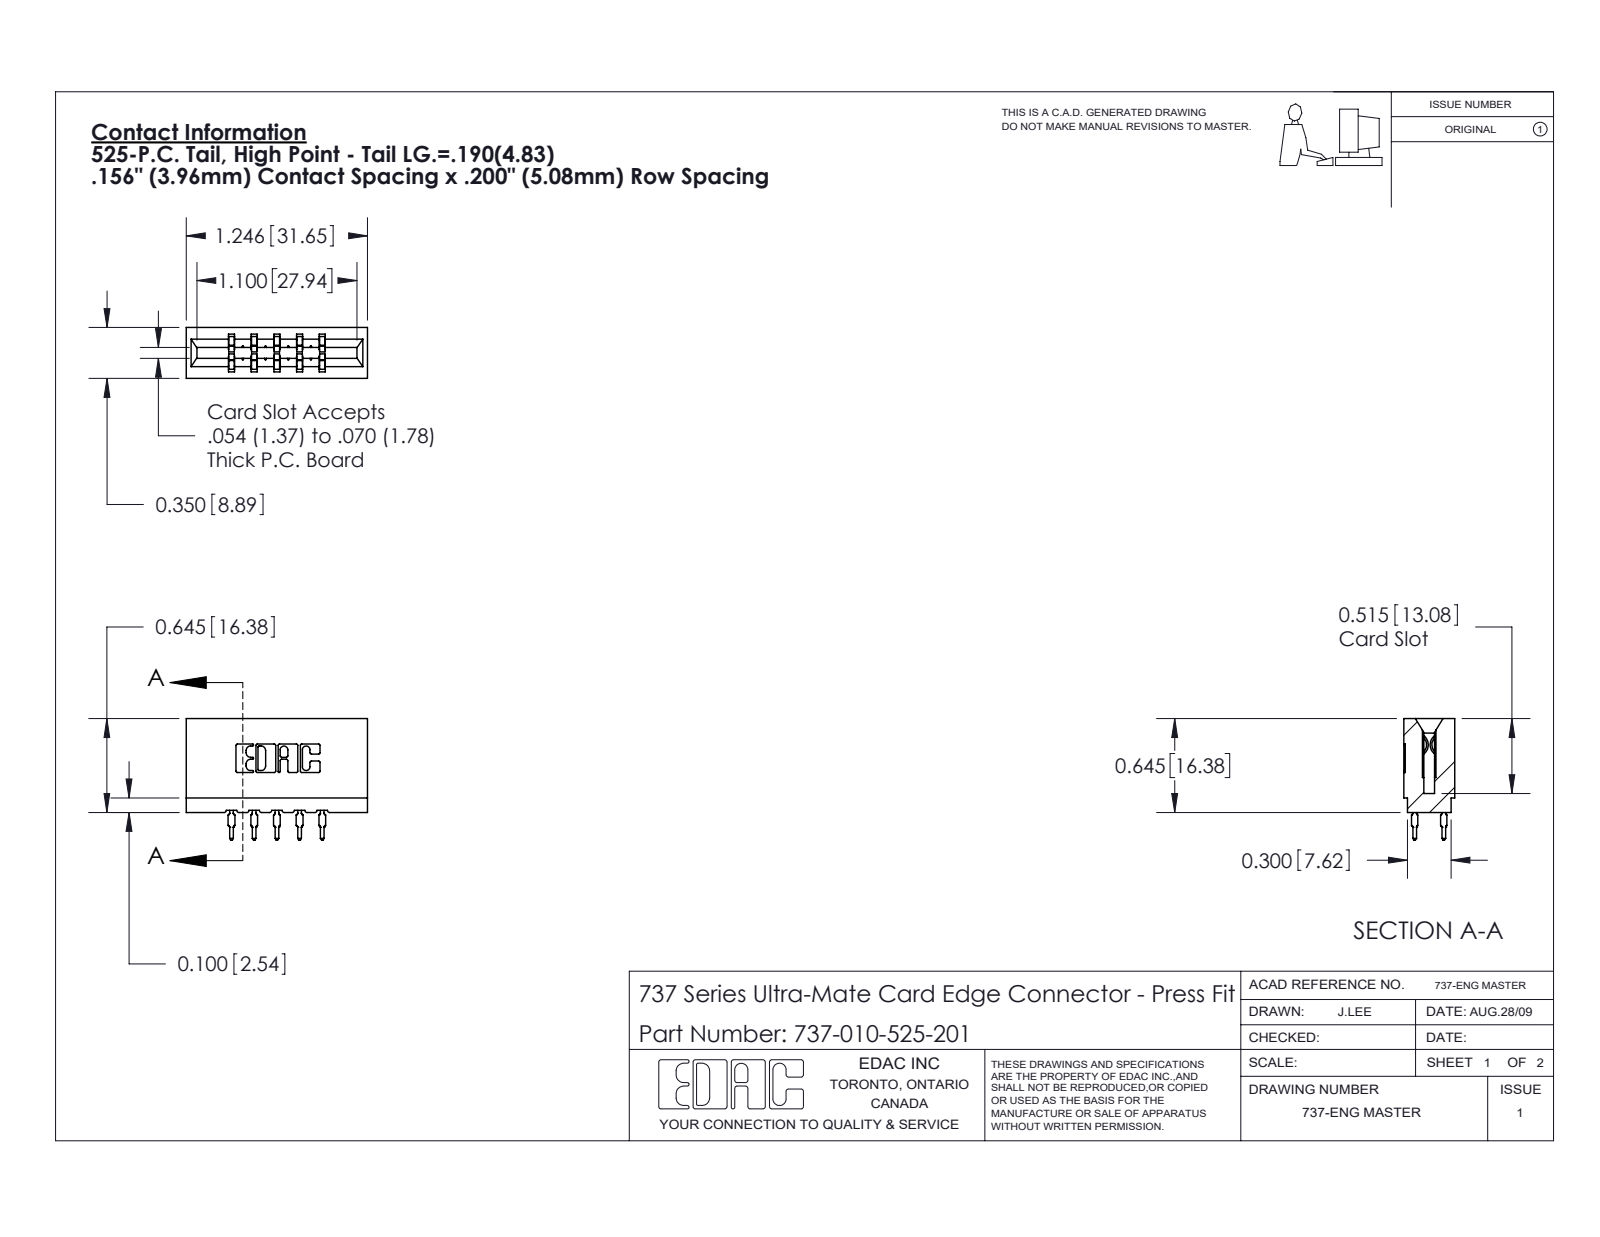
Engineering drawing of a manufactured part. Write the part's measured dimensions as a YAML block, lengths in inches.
part_name: "737 Part_Insulator Option - 01; 745-292-001_525; 737-010-525-201"
step_written_by: "SolidWorks 2020 (CONFIG_CONTROL_DESIGN)"
units: inches
bodies: {solids: 11, faces: 994, planar: 519, cylindrical: 215, other: 260}
overall_size: [1.246, 0.836, 0.35]
volume: 0.205
surface_area: 6.273
partial_cylinders:
  - {radius: 0.01, count: 22}
  - {radius: 0.021, count: 20}
  - {radius: 0.015, count: 10}
  - {radius: 0.005, count: 8}
  - {radius: 0.011, count: 8}
  - {radius: 0.007, count: 6}
  - {radius: 0.031, count: 6}
  - {radius: 0.026, count: 3}
face_to_face_distances: [0.138, 0.212, 0.156, 0.35, 0.312, 0.198, 0.074, 0.354, 0.042, 0.025]
